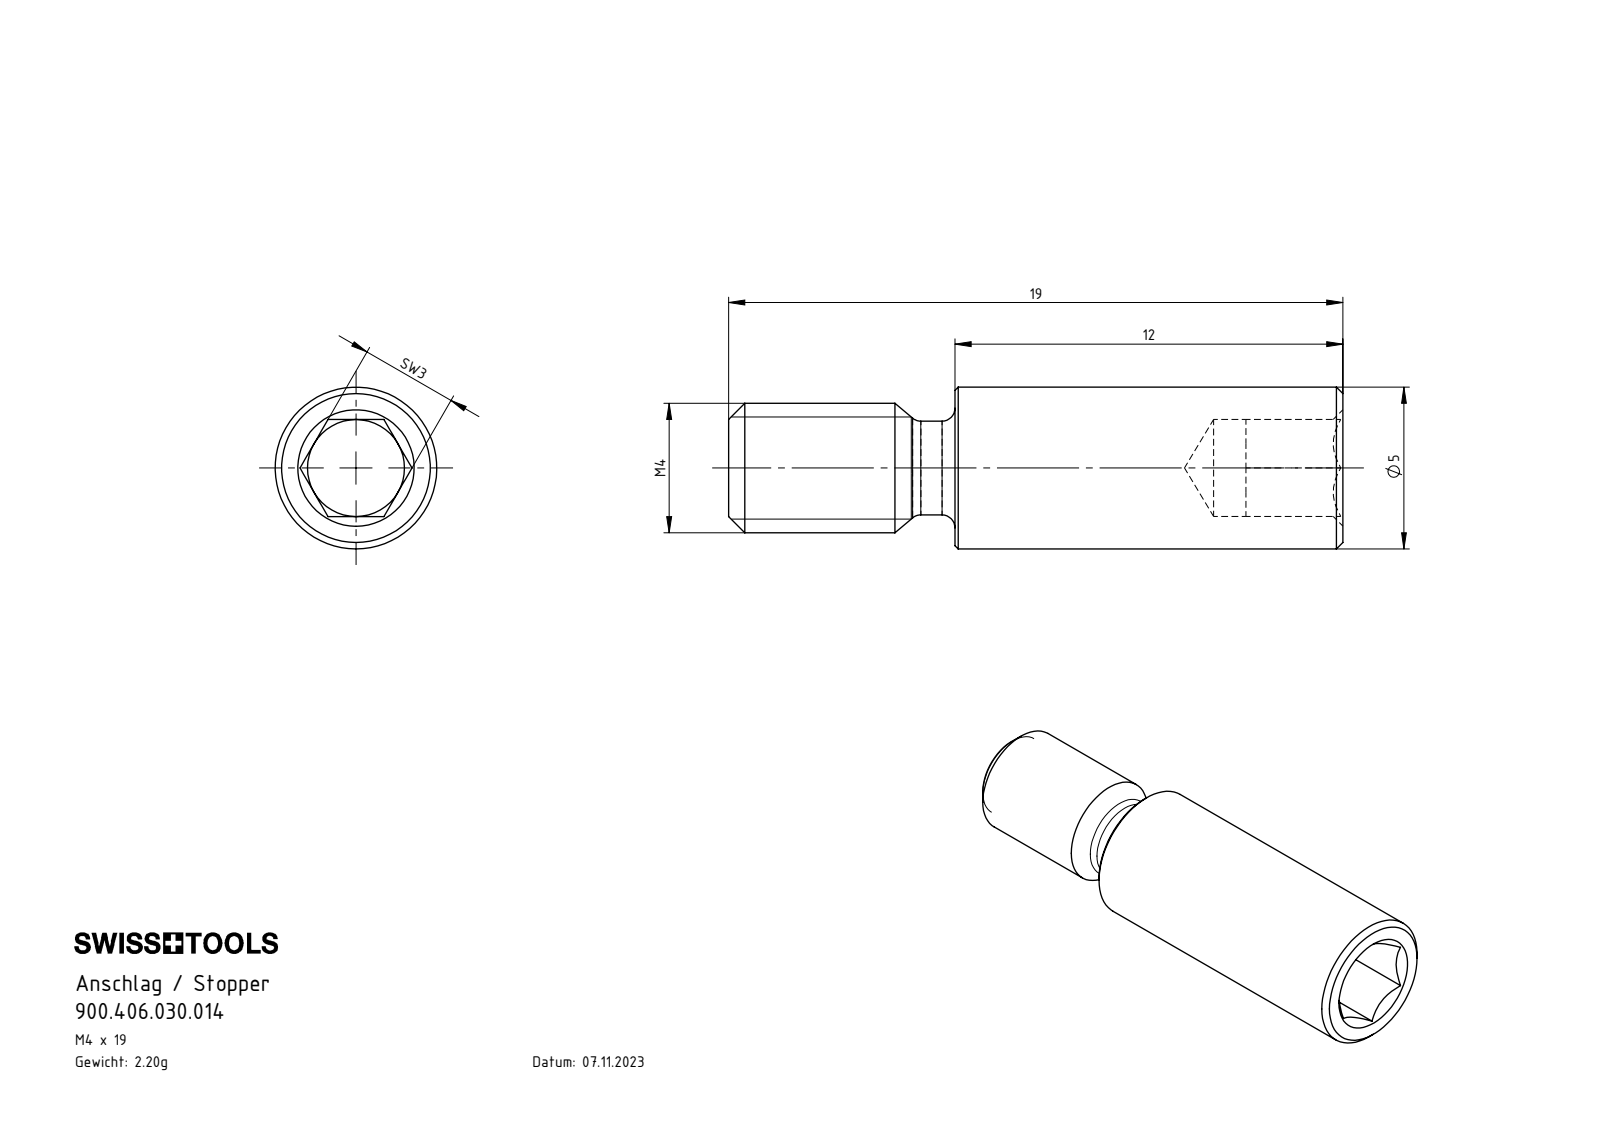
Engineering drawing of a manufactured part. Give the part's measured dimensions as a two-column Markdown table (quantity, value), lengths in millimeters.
| quantity | value |
| --- | --- |
| part name | 900.406.030.014 |
| STEP written by | SolidWorks 2022 (AUTOMOTIVE_DESIGN) |
| units | millimeters |
| bodies | 1 solid, 39 faces (15 planar, 8 cylindrical, 16 other) |
| overall size | 19 × 5 × 5 |
| volume | 280 mm³ |
| surface area | 351 mm² |
| round holes (diameter × count) | 3 × 1 |
| round bosses / shafts (diameter × count) | 5 × 1, 4 × 1, 2.9 × 1 |
| main face-to-face distances | 3, 7, 19, 12, 16, 9 |
